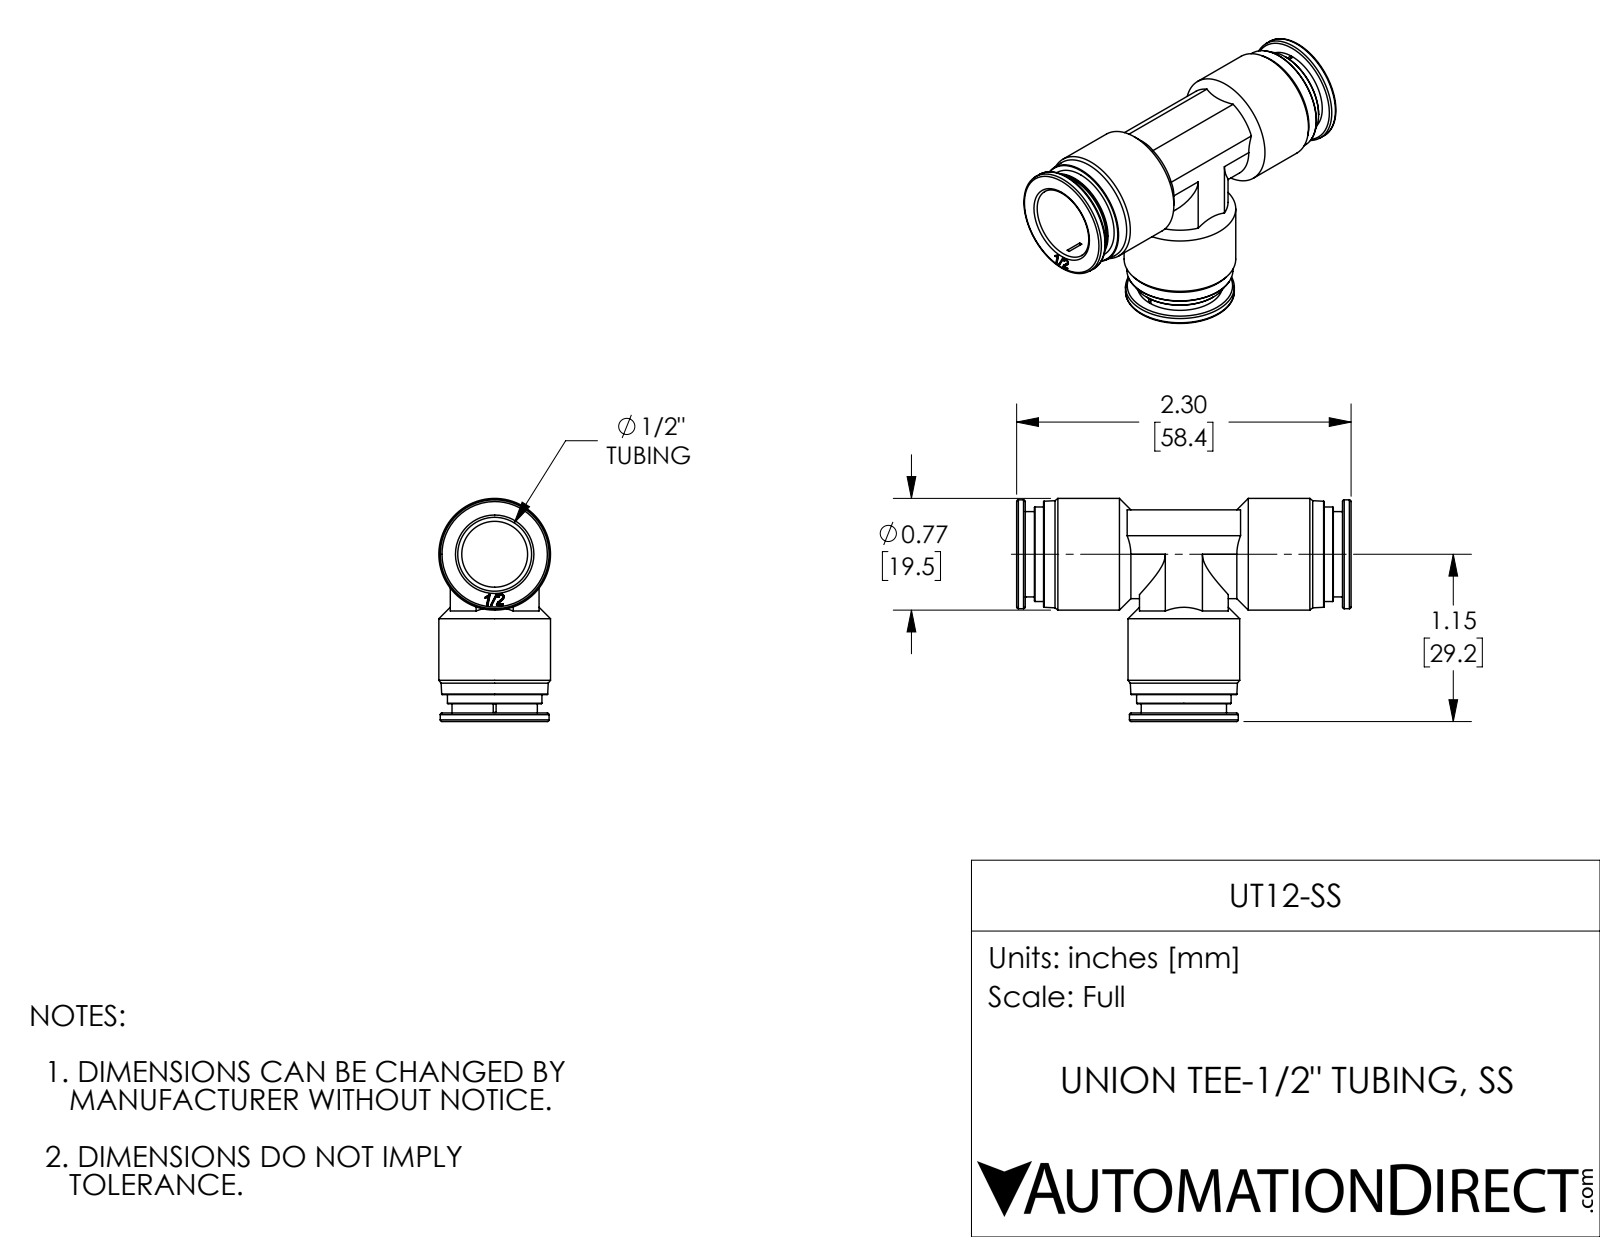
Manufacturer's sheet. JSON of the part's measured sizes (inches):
{"part_name": "UT12-SS", "step_written_by": "SolidWorks 2017 (AUTOMOTIVE_DESIGN)", "units": "inches", "bodies": {"solids": 1, "faces": 240, "planar": 89, "cylindrical": 49, "other": 102}, "overall_size": [2.299, 1.533, 0.768], "volume_in3": 0.622, "surface_area_in2": 14.33, "round_holes": [[0.453, 2], [0.508, 2], [0.594, 2]], "round_bosses_or_shafts": [[0.768, 2], [0.748, 2], [0.65, 2], [0.587, 2]], "partial_cylinders_radius": [[0.331, 2], [0.305, 1]], "face_to_face_distances": [0.059, 2.24, 0.185, 0.126, 1.455, 0.61, 2.055, 1.396, 2.299, 2.114]}
